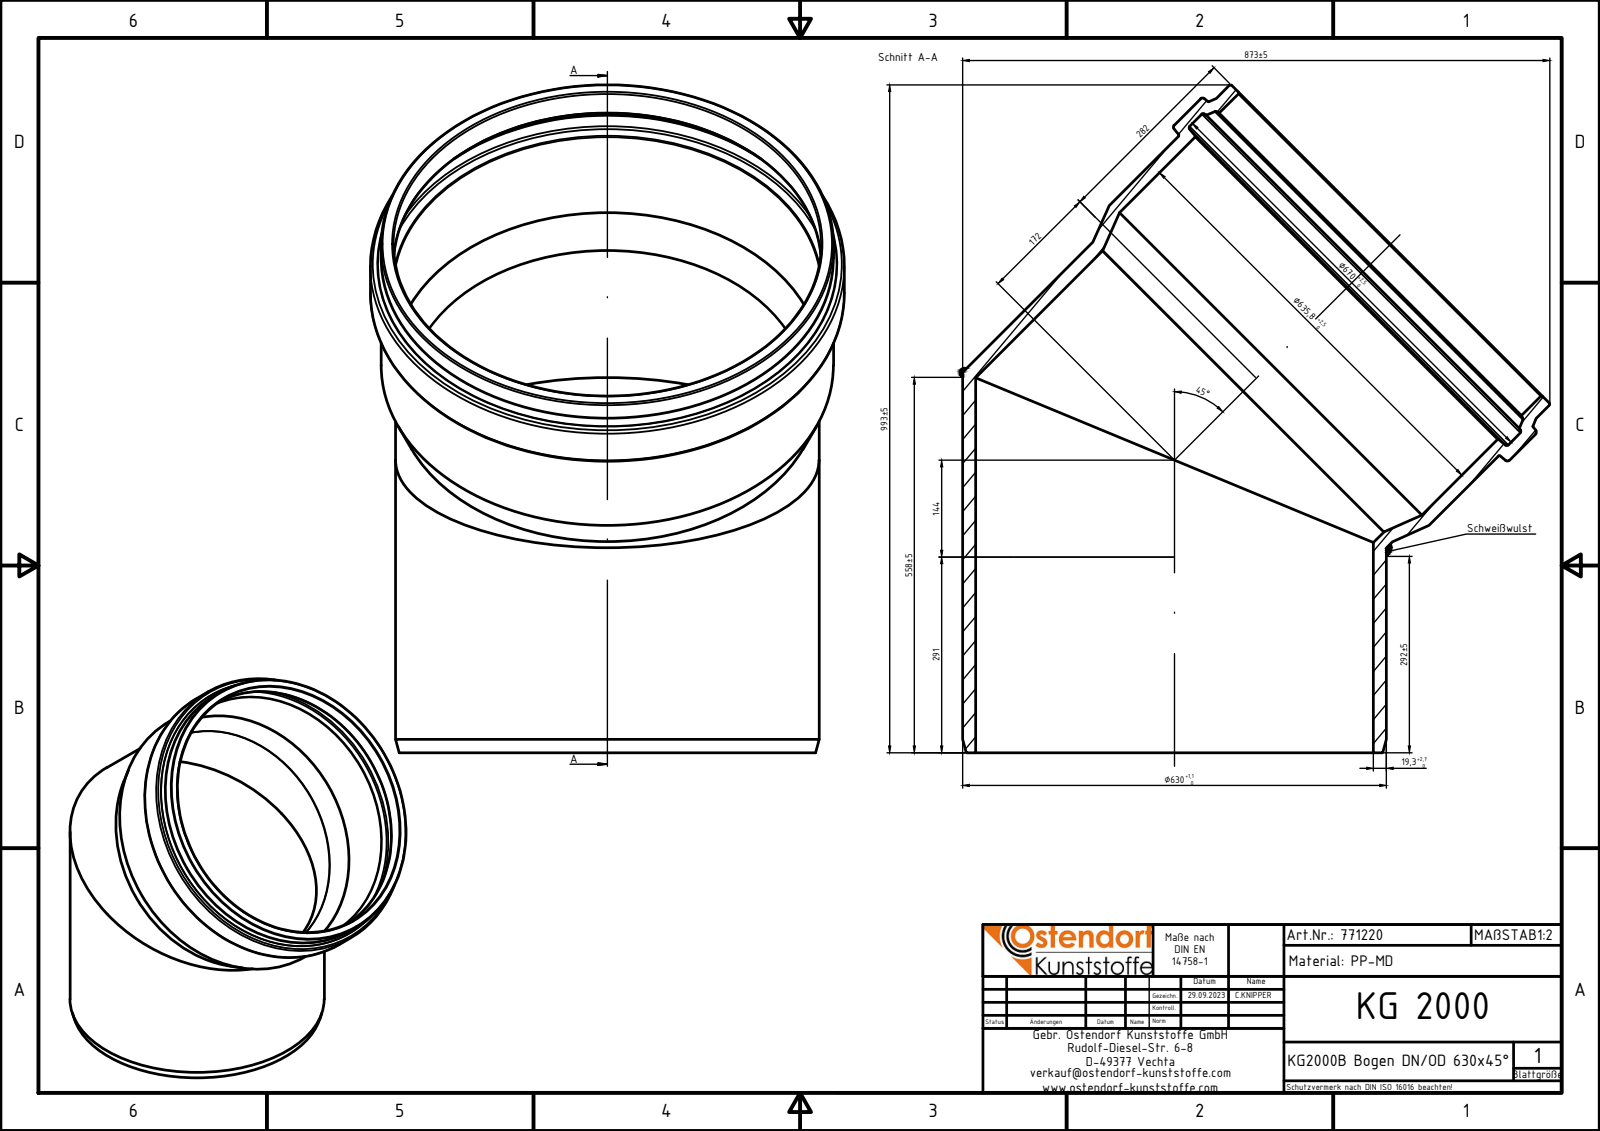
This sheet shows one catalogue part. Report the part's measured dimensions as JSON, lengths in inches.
{"part_name": "KGB DN630x45° KG2000 - Zusammenbau; KGB DN630x45° KG2000 - Teil 1; KGB DN630x45° KG2000 - Teil 2", "step_written_by": "Autodesk Inventor 2021 (AUTOMOTIVE_DESIGN)", "units": "inches", "bodies": {"solids": 2, "faces": 38, "planar": 4, "cylindrical": 10, "other": 24}, "overall_size": [39.076, 35.472, 27.677], "volume_in3": 2055, "surface_area_in2": 5746, "round_holes": [[23.236, 2], [24.98, 1], [25.059, 1], [26.417, 1]], "round_bosses_or_shafts": [[24.803, 2], [27.677, 1], [26.429, 1], [26.35, 1]]}
